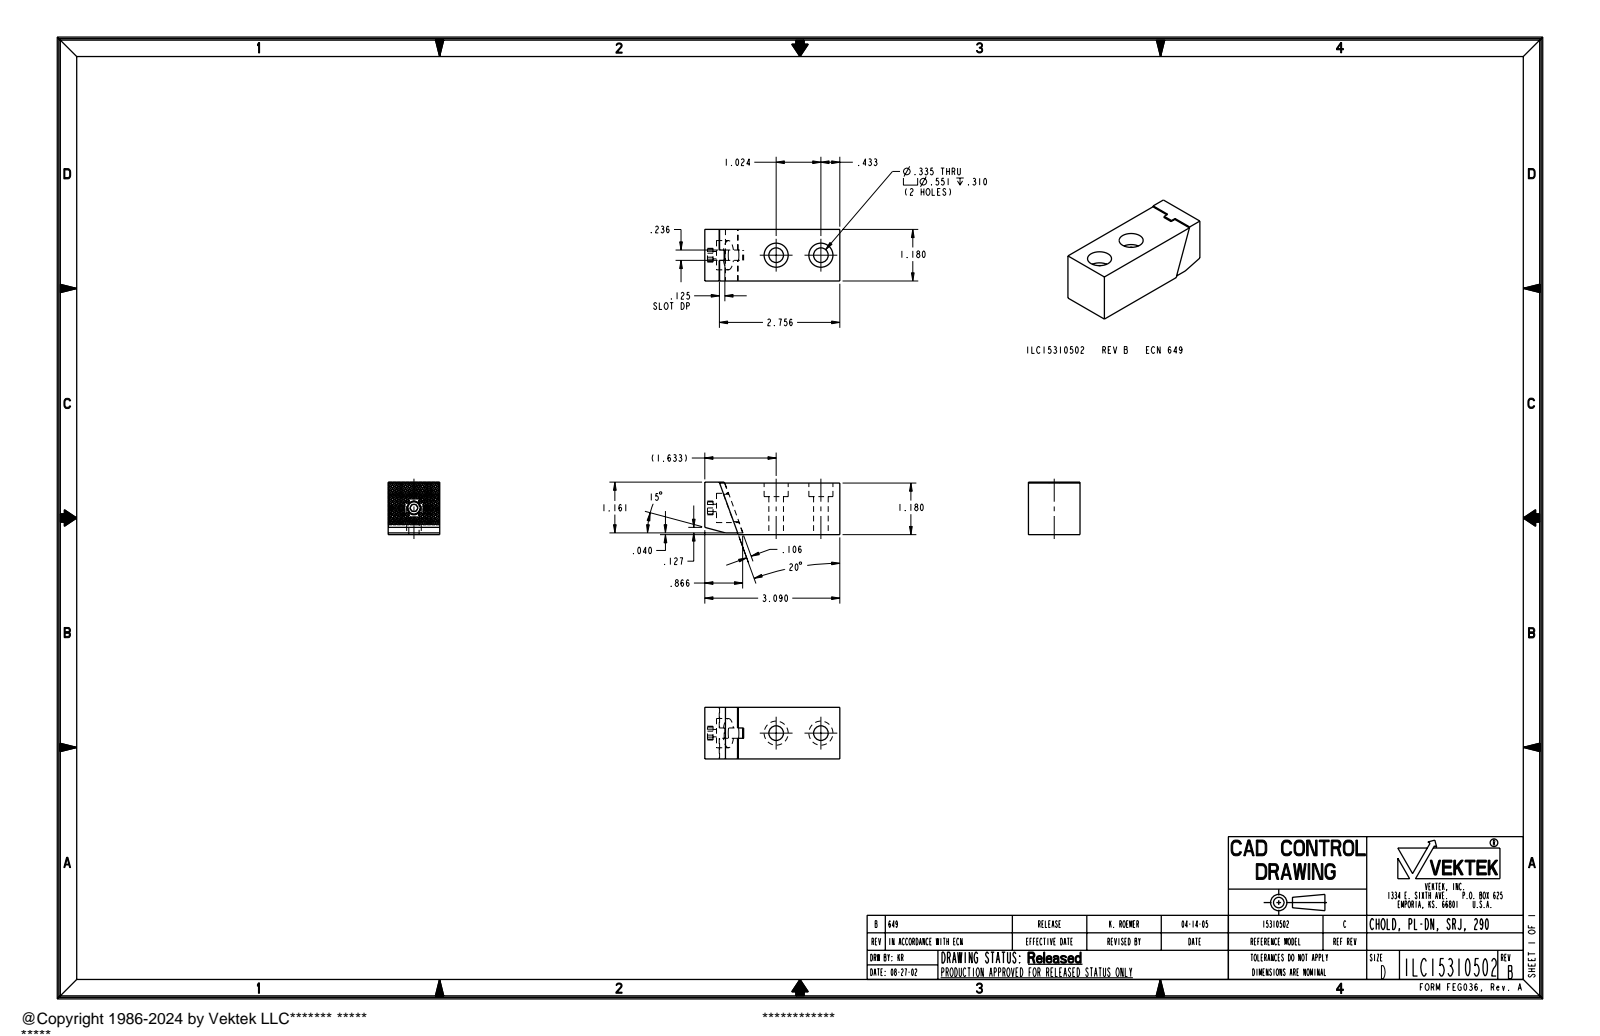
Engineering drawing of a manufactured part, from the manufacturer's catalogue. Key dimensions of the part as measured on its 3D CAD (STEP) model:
Part name (STEP PRODUCT): ILC15310502
STEP written by: PRO/ENGINEER BY PARAMETRIC TECHNOLOGY CORPORATION, 2004290 (AUTOMOTIVE_DESIGN_CC2)
Units: inches
Bodies: 1 solid, 63 faces (47 planar, 16 cylindrical, 0 other)
Overall size (bounding box): 3.09 × 1.201 × 1.181
Volume: 3.811 in³ · Surface area: 21.86 in²
Round holes (diameter × count): ⌀0.335 ×2, ⌀0.551 ×2, ⌀0.169 ×1, ⌀0.315 ×1, ⌀0.669 ×1
Round bosses / shafts (diameter × count): ⌀0.276 ×1
Main face-to-face distances: 1.18, 1.18, 1.181, 3.09, 1.181, 1.202, 0.022, 0.04, 1.14, 1.161
Hole centre spacings: 1.024
